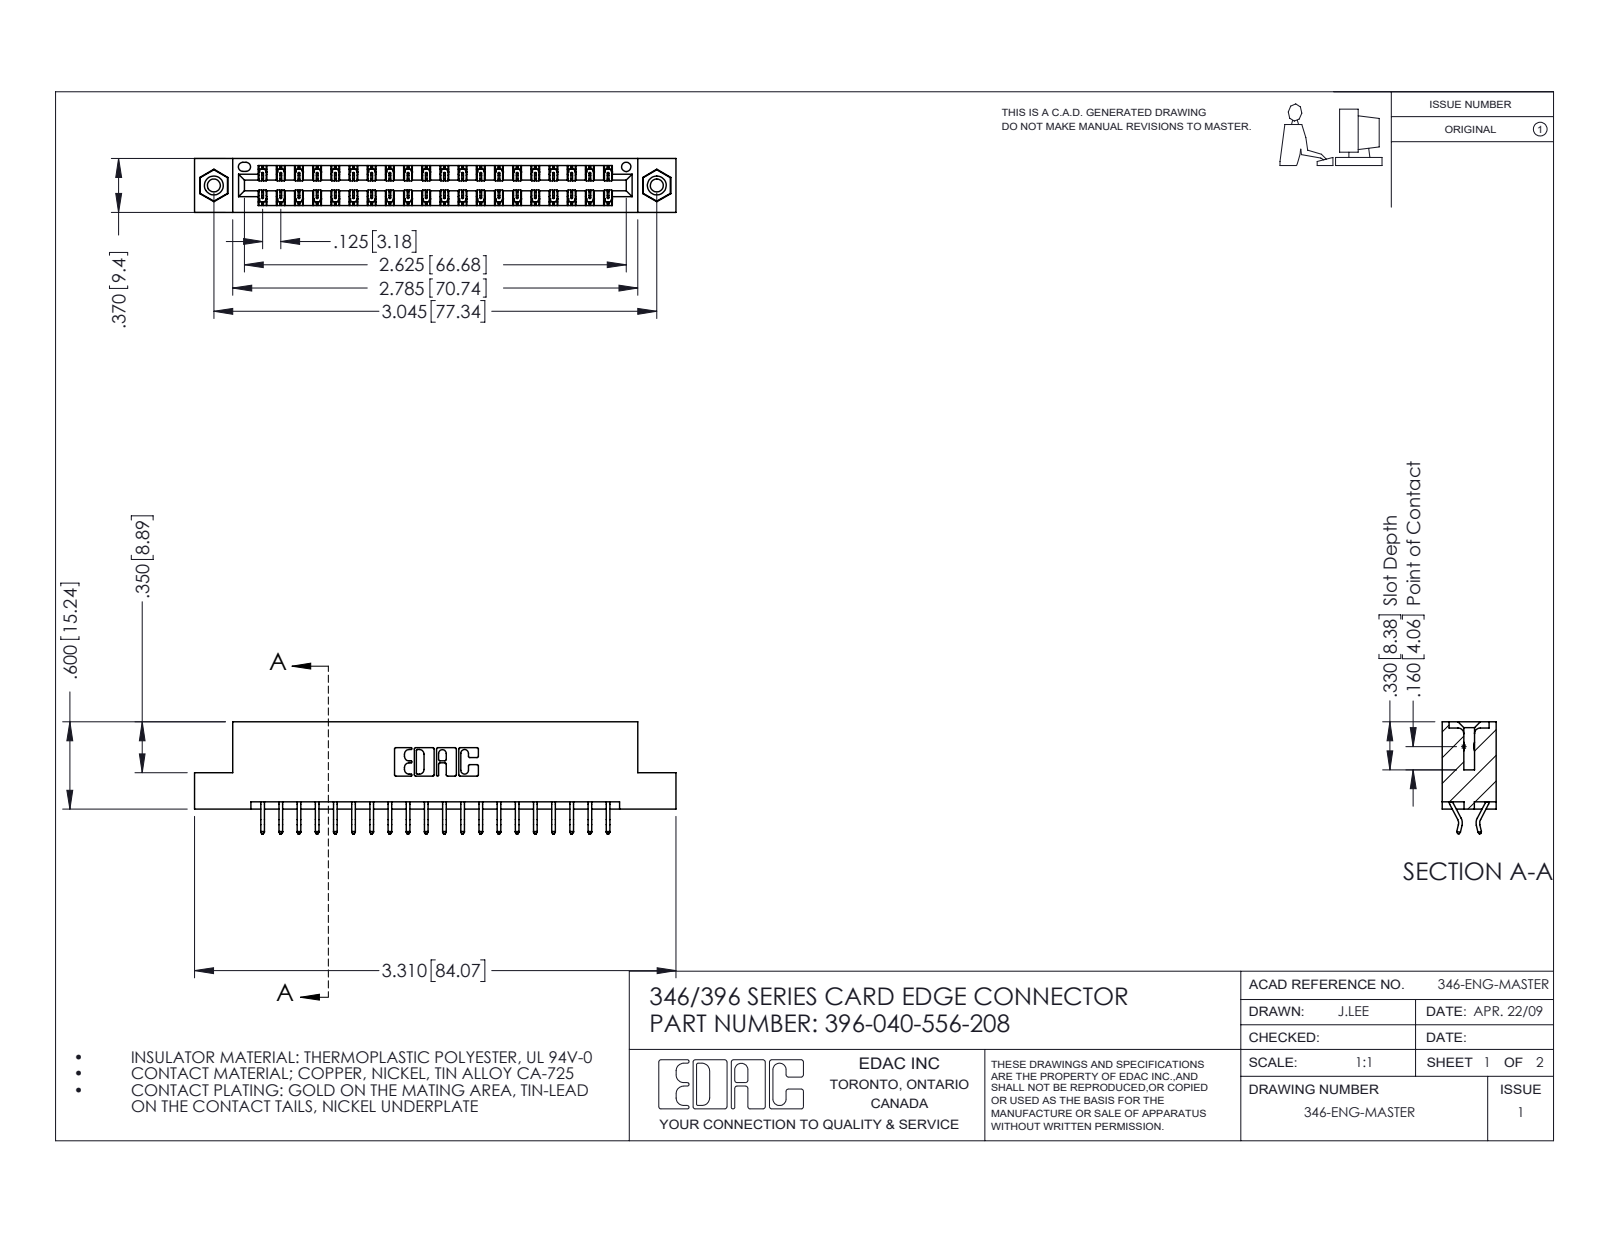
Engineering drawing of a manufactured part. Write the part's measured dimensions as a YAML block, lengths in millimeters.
part_name: "345-292-001_556 Tail; 345-250-001_345-250-003-102; 346 Part_Flush Mounting Lugs - 0.156 Dia-TI; 396-040-556-208"
step_written_by: "SolidWorks 2016 (CONFIG_CONTROL_DESIGN)"
units: millimeters
bodies: {solids: 43, faces: 2502, planar: 1668, cylindrical: 818, other: 16}
overall_size: [84.1, 19.6, 9.4]
volume: 8010
surface_area: 10660
round_holes:
  - {diameter: 2.3, count: 2}
  - {diameter: 3.2, count: 2}
  - {diameter: 4, count: 2}
  - {diameter: 1.6, count: 1}
round_bosses_or_shafts:
  - {diameter: 3.9, count: 2}
partial_cylinders:
  - {radius: 0.2, count: 60}
  - {radius: 0.3, count: 22}
  - {radius: 0.2, count: 6}
  - {radius: 0.8, count: 6}
  - {radius: 0.7, count: 3}
  - {radius: 0.3, count: 2}
  - {radius: 0.4, count: 2}
  - {radius: 0.6, count: 2}
face_to_face_distances: [1.2, 8.2, 9.4, 6.4, 0.6, 1.8, 7.6, 7, 3.8, 5.6]
hole_center_spacings: [6.2, 72.1, 77.3]
